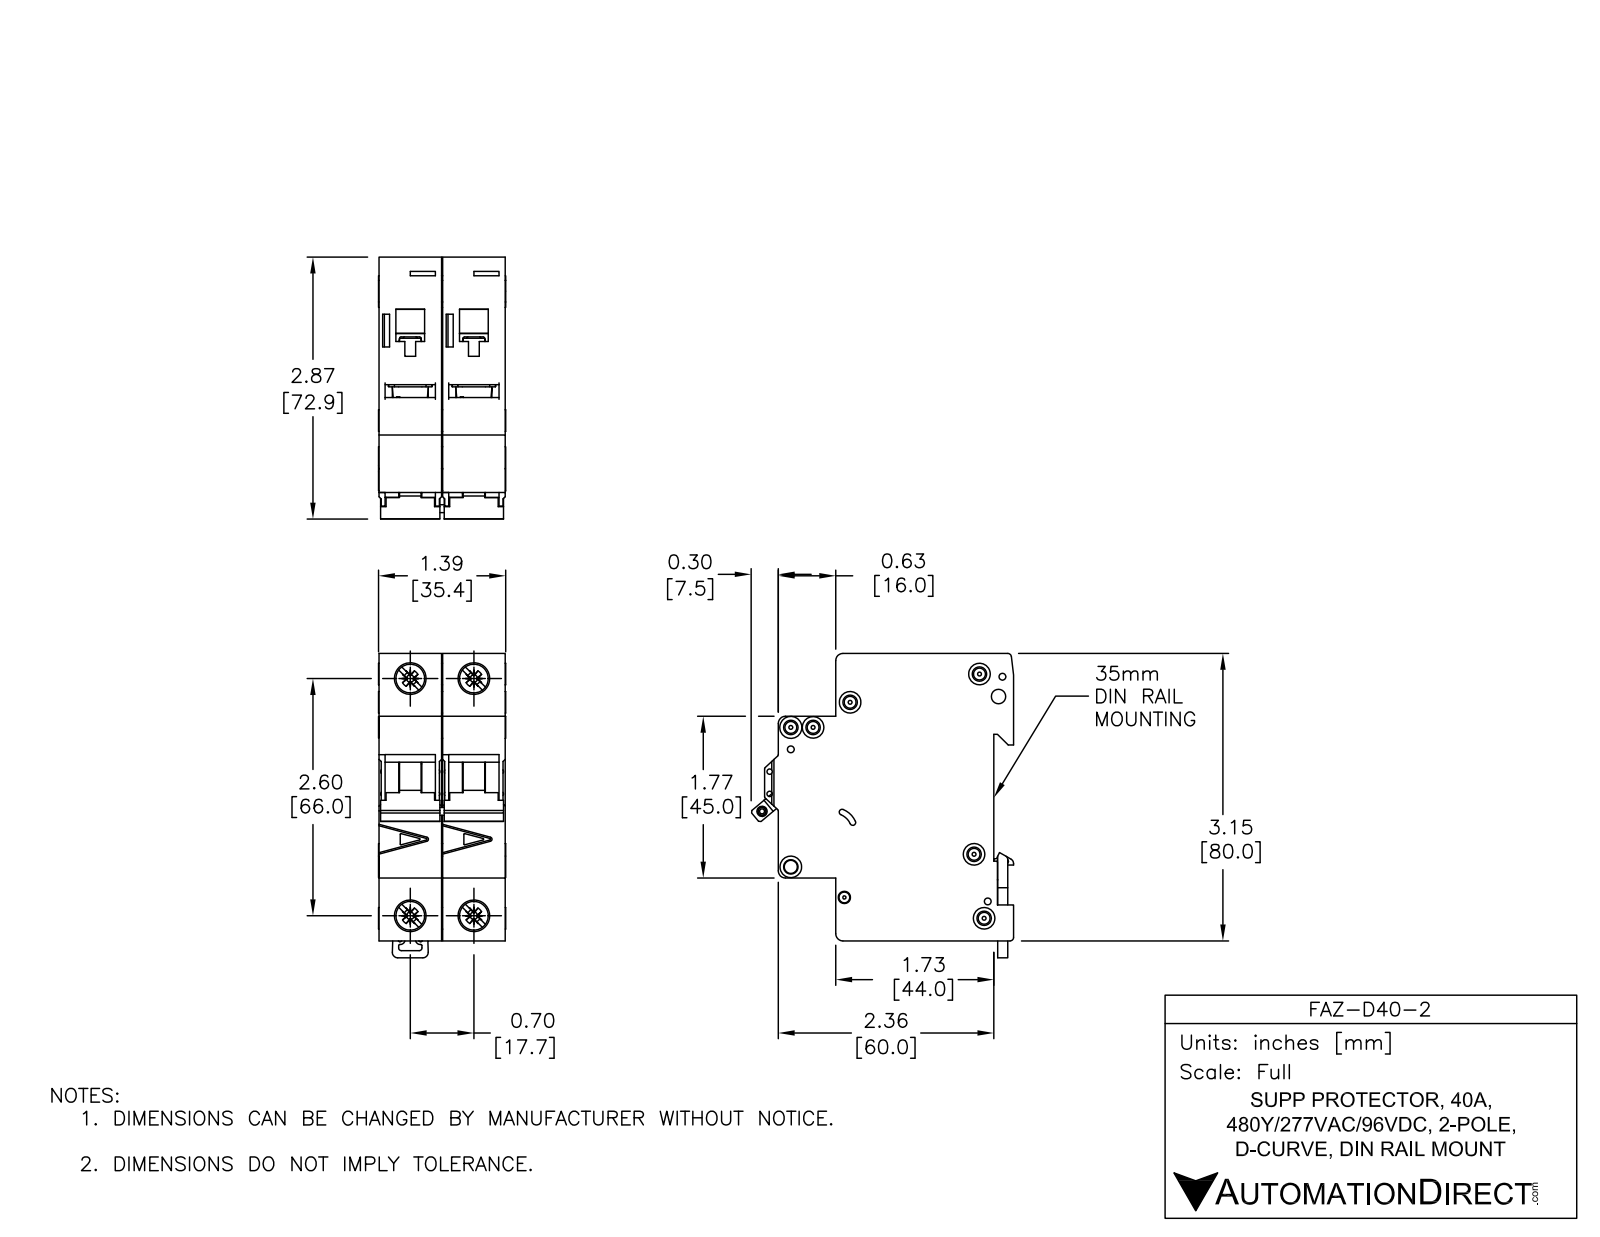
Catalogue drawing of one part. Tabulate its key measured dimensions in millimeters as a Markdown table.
| quantity | value |
| --- | --- |
| part name | FAZ-D40-2 |
| STEP written by | SolidWorks 2014 (AUTOMOTIVE_DESIGN) |
| units | millimeters |
| bodies | 8 solids, 1104 faces (466 planar, 396 cylindrical, 242 other) |
| overall size | 84.78 × 73.04 × 35.4 |
| volume | 149 808 mm³ |
| surface area | 38 799 mm² |
| round holes (diameter × count) | 3.6 × 6, 1.9 × 3, 1.09 × 2, 1.5 × 2, 4 × 2, 7.15 × 2, 8.2 × 2, 2.15 × 1, 2.2 × 1, 2.55 × 1, 3.3 × 1, 3.4 × 1 |
| round bosses / shafts (diameter × count) | 6 × 4, 8.2 × 2, 2.5 × 2 |
| partial cylindrical surfaces (radius × count) | 0.25 × 49, 0.5 × 19, 2 × 10, 0.2 × 8, 1 × 8, 0.8 × 2, 1.8 × 2, 3 × 2 |
| main face-to-face distances | 17.7, 17.5, 35.2, 79.48, 5.5, 49.5, 44, 65.5, 60, 16 |
| hole center spacings | 6.2, 13.64, 17.7, 66, 68.33, 4.81, 5.19, 5.61 |
